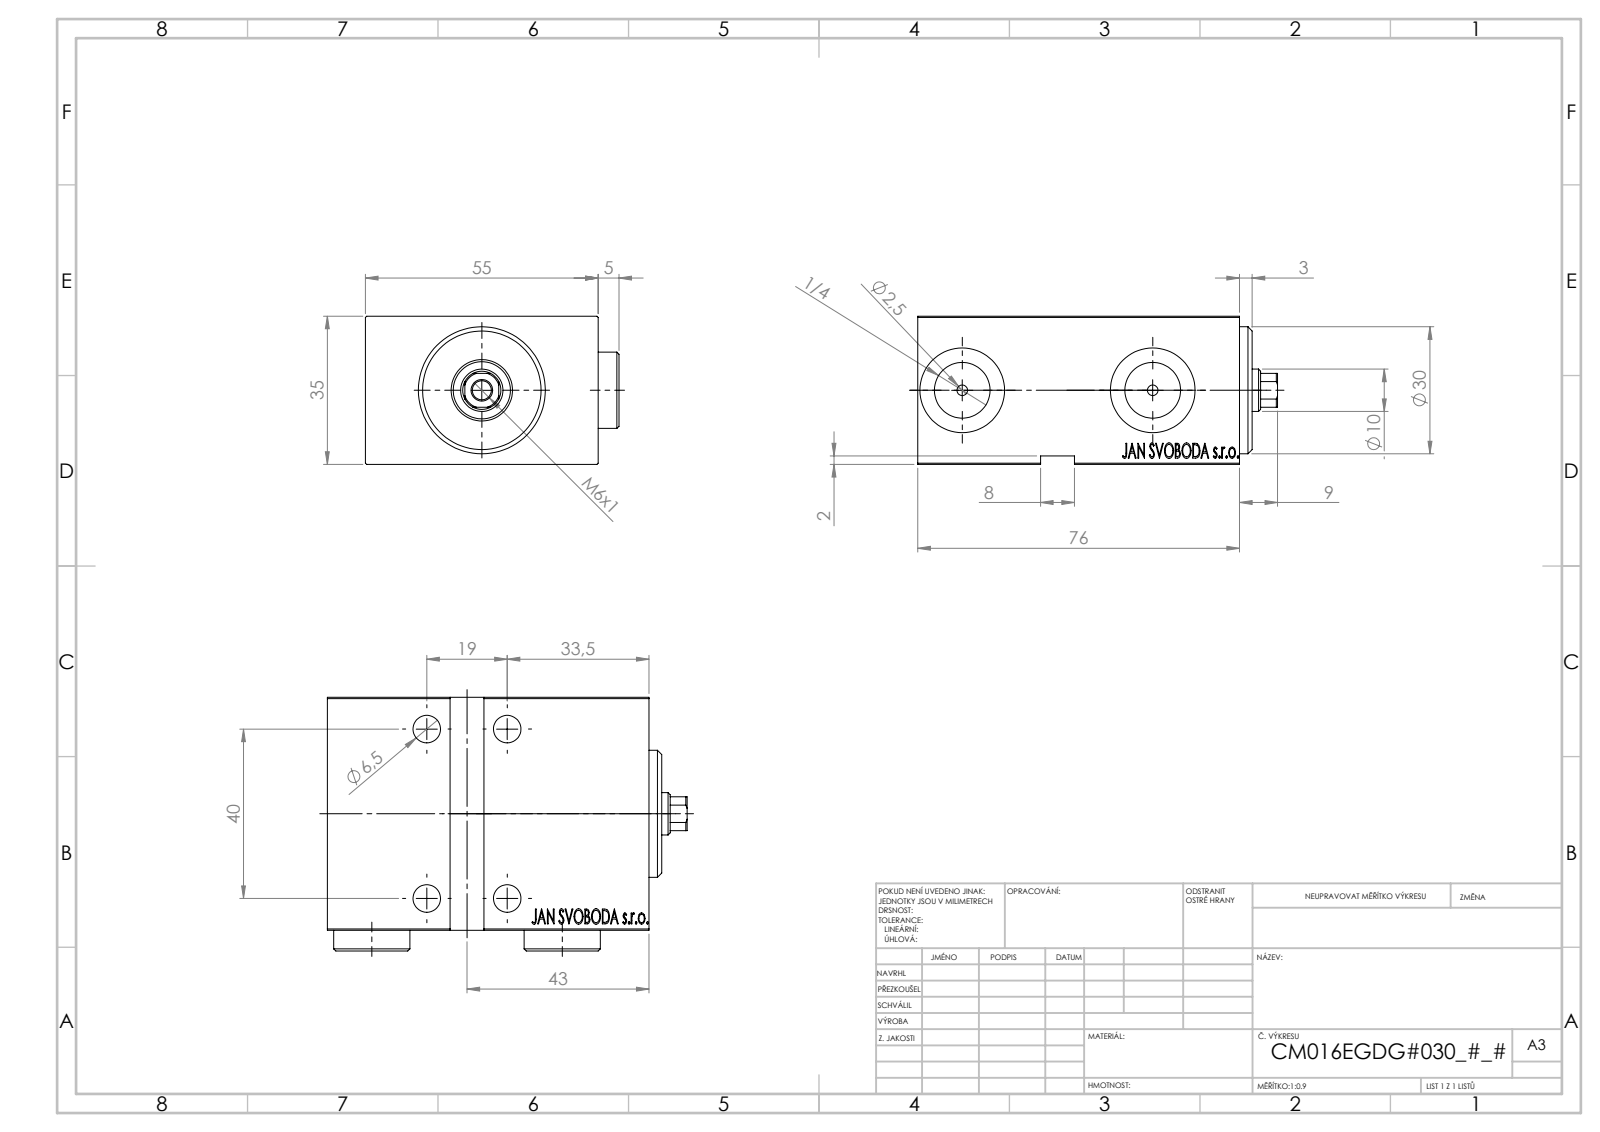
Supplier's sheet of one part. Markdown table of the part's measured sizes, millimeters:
| quantity | value |
| --- | --- |
| part name | V450CM_E_VCP; V450CM_VC_B; V450CM_E_Body; Zatka_OIL_PORT |
| STEP written by | SolidWorks 2019 (CONFIG_CONTROL_DESIGN) |
| units | millimeters |
| bodies | 5 solids, 913 faces (445 planar, 70 cylindrical, 398 other) |
| overall size | 85 × 59.9 × 35 |
| volume | 133 610 mm³ |
| surface area | 35 390 mm² |
| round holes (diameter × count) | 6.5 × 4, 10.5 × 4, 2.5 × 2, 13.16 × 2, 20 × 2, 4.5 × 1, 10 × 1, 13.5 × 1, 14.5 × 1, 16 × 1, 25 × 1 |
| round bosses / shafts (diameter × count) | 18 × 3, 30 × 1 |
| partial cylindrical surfaces (radius × count) | 4.5 × 1 |
| main face-to-face distances | 35, 55, 76, 5, 54.9, 71, 42, 8, 3, 2 |
| hole center spacings | 19, 40, 44.28, 45 |
